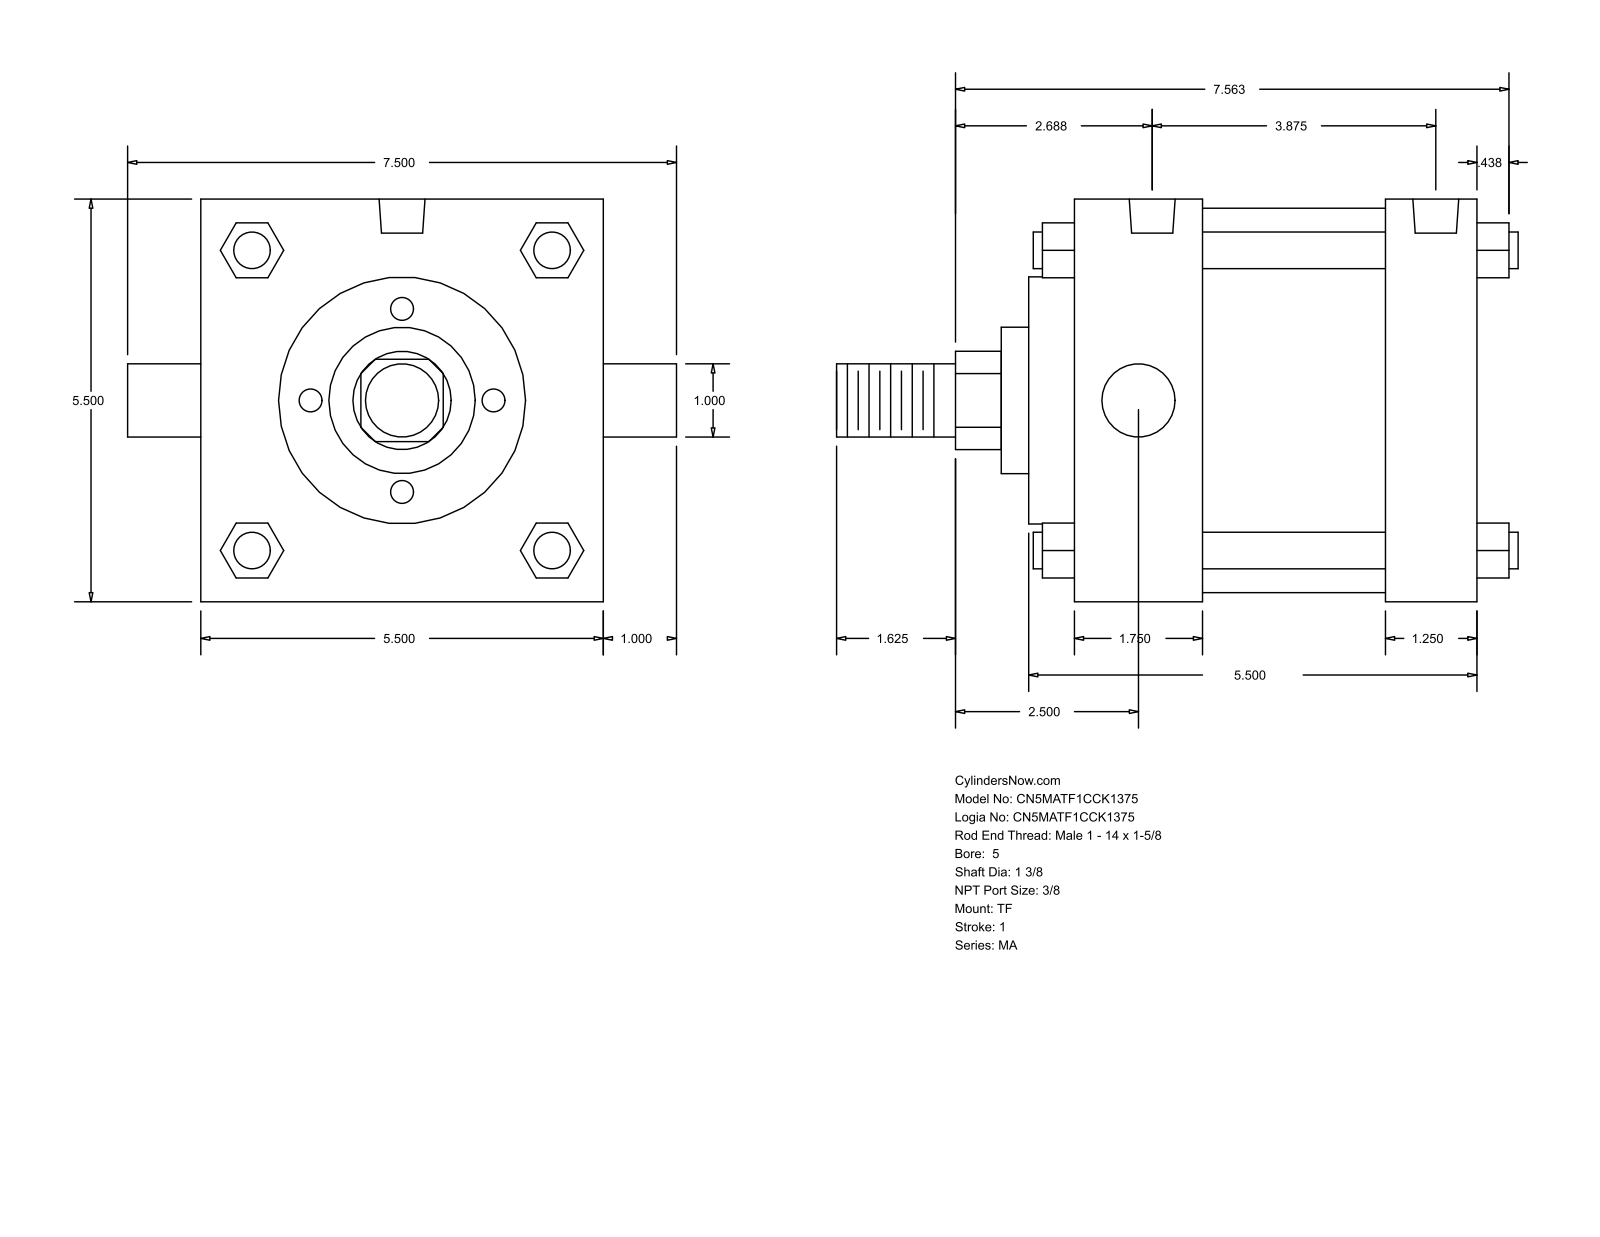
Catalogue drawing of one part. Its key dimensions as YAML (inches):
part_name: "MA_TF__0500_1.375"
step_written_by: "GSSL Pune (CONFIG_CONTROL_DESIGN)"
units: inches
bodies: {solids: 0, faces: 122, planar: 93, cylindrical: 29, other: 0}
overall_size: [9.313, 7.5, 5.5]
round_holes:
  - {diameter: 0.437, count: 3}
  - {diameter: 0.627, count: 2}
round_bosses_or_shafts:
  - {diameter: 0.5, count: 4}
  - {diameter: 1, count: 2}
  - {diameter: 5.25, count: 1}
  - {diameter: 3.375, count: 1}
  - {diameter: 2, count: 1}
  - {diameter: 1.375, count: 1}
partial_cylinders:
  - {radius: 0.672, count: 1}
face_to_face_distances: [5.5, 4.25, 1.25, 1.75, 2.5, 3.75, 0.625, 2.375, 4.875, 6.125]
hole_center_spacings: [0.187, 0.188, 3.5, 3.687, 3.688, 3.875]
